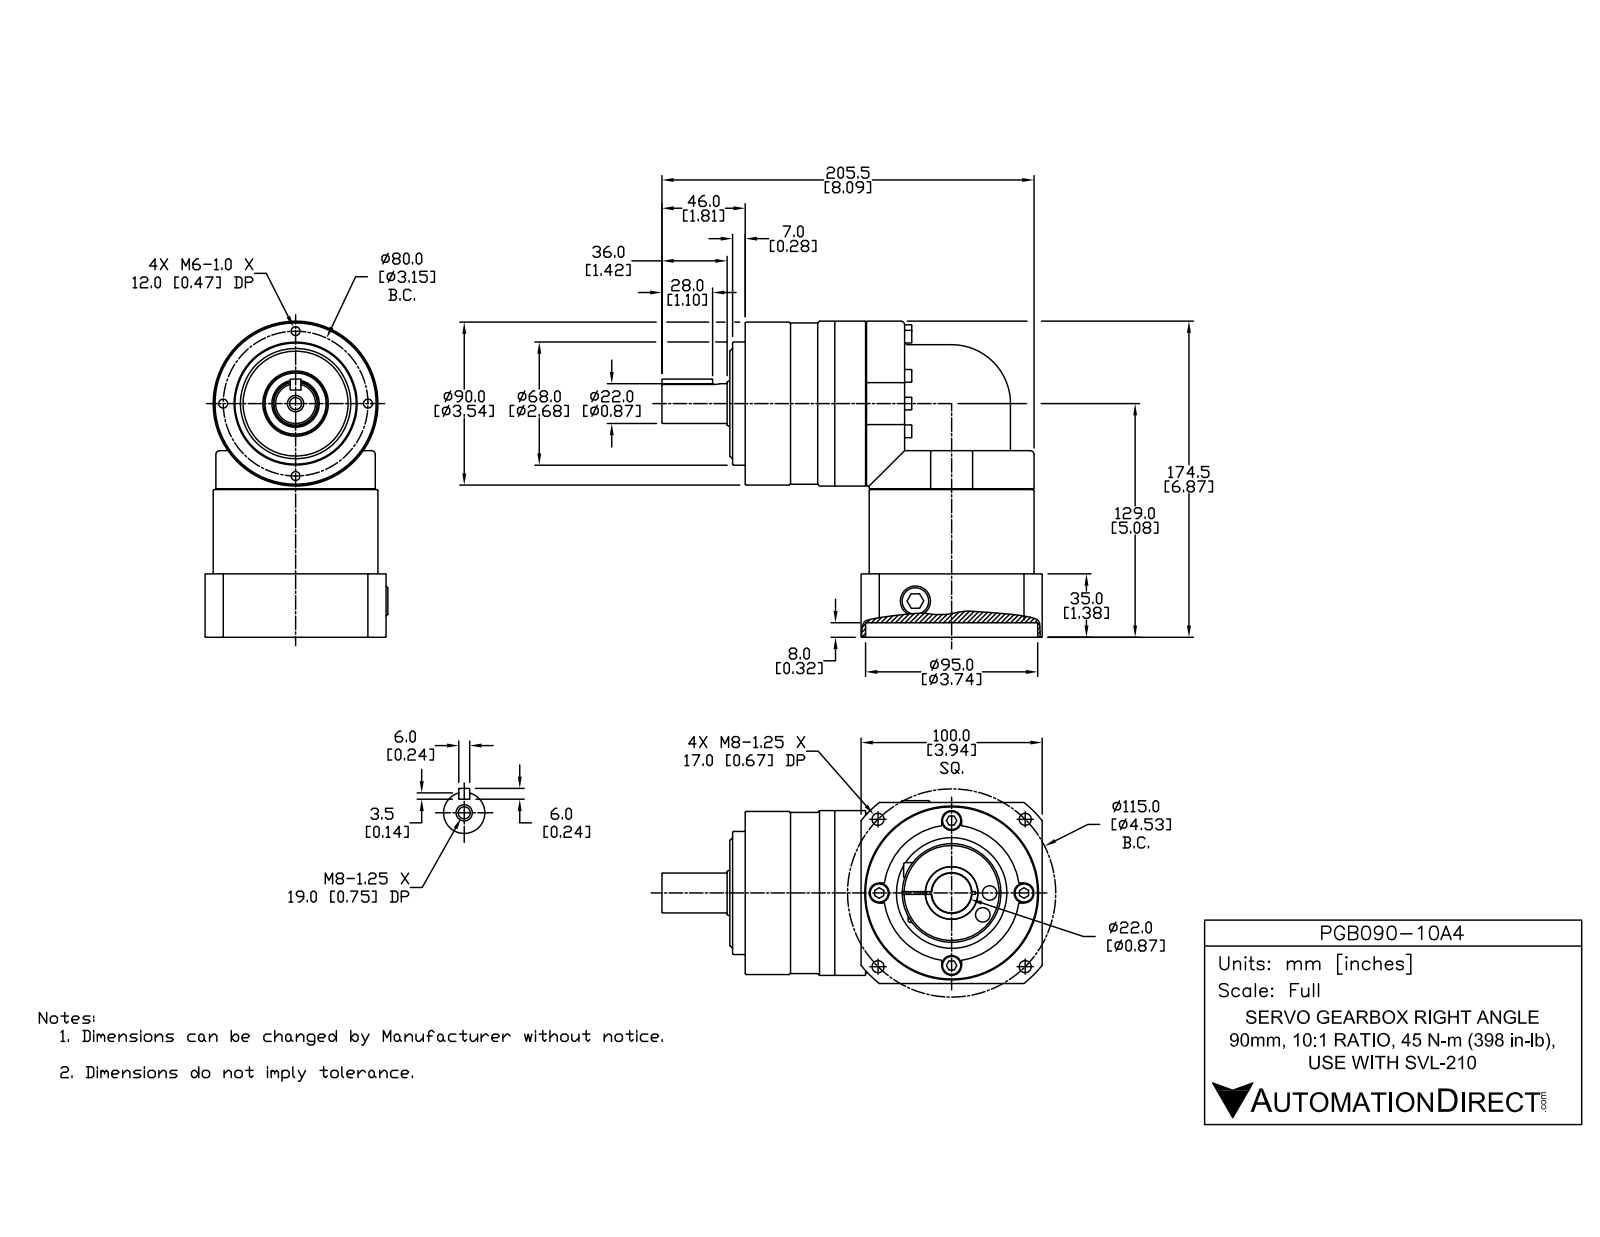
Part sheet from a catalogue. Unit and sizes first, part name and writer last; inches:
Units: inches
Overall size (bounding box): 8.268 × 6.87 × 3.976
Round holes (diameter × count): ⌀0.194 ×4, ⌀0.262 ×4, ⌀0.433 ×4, ⌀0.315 ×2, ⌀0.262 ×1, ⌀0.346 ×1, ⌀0.561 ×1, ⌀0.866 ×1, ⌀2.402 ×1, ⌀2.953 ×1, ⌀3.74 ×1
Round bosses / shafts (diameter × count): ⌀0.276 ×9, ⌀0.394 ×4, ⌀3.583 ×2, ⌀3.465 ×2, ⌀3.543 ×1, ⌀3.504 ×1, ⌀2.677 ×1, ⌀2.146 ×1
Partial cylindrical surfaces — rounded edges, fillets, slot ends (radius × count): R0.079 ×6, R1.28 ×2, R0.118 ×1, R0.131 ×1, R0.276 ×1, R2.52 ×1
Main face-to-face distances: 3.937, 0.276, 1.102, 1.063, 0.315, 6.457, 2.52, 3.74, 1.378, 0.689
Hole centre spacings: 1.575, 1.601, 2.227, 3.556, 2.264, 3.15, 3.202, 0.827
Volume: 84.76 in³ · Surface area: 189.9 in²
Bodies: 1 solid, 511 faces (216 planar, 130 cylindrical, 165 other)
Part name (STEP PRODUCT): PGB090-10A4
STEP written by: SolidWorks 2014 (AUTOMOTIVE_DESIGN)
